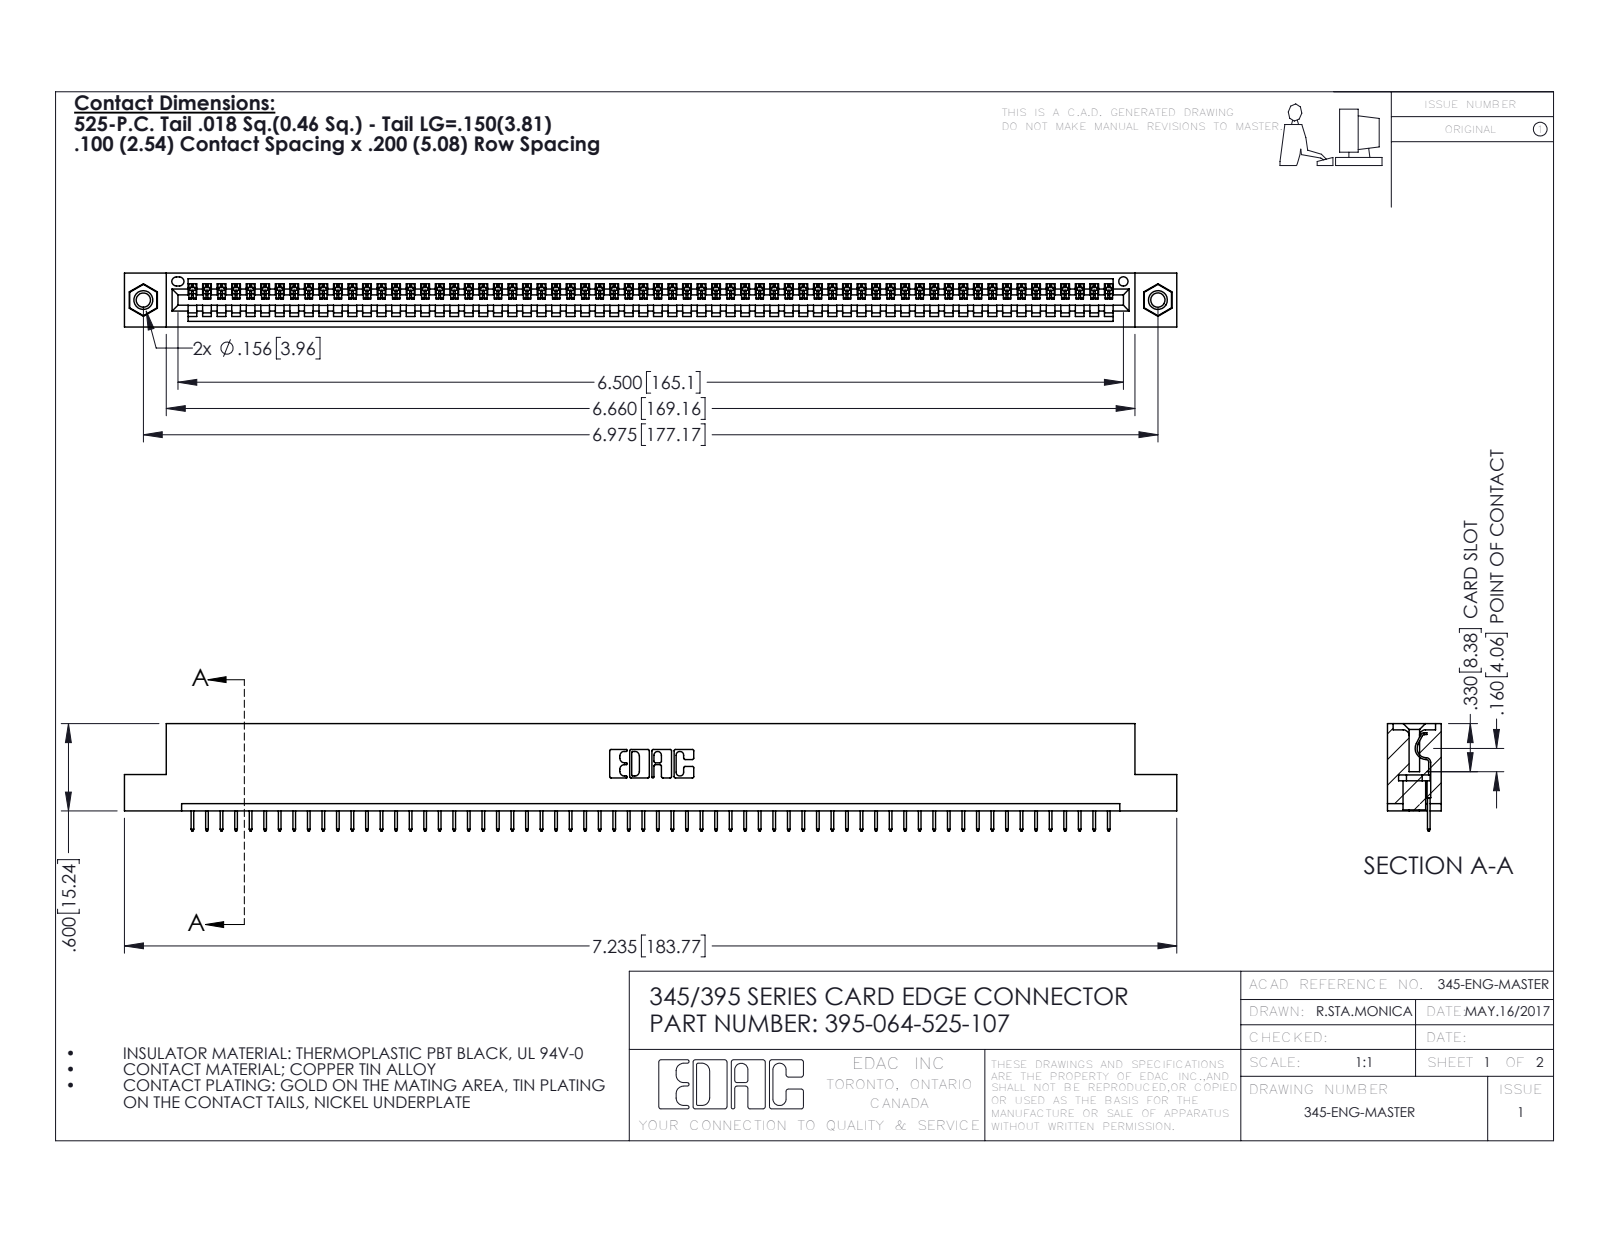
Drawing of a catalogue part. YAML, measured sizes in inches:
part_name: "395-064-525-107; 345-292-001_345-293-125; 345 Part_Flush Mounting Lugs - 0.156 Dia-TI; 345-250-001_345-250-005-103"
step_written_by: "SolidWorks 2020 (CONFIG_CONTROL_DESIGN)"
units: inches
bodies: {solids: 67, faces: 4154, planar: 3056, cylindrical: 1082, other: 16}
overall_size: [7.235, 0.737, 0.37]
volume: 1.059
surface_area: 34.92
round_holes:
  - {diameter: 0.098, count: 2}
  - {diameter: 0.125, count: 2}
  - {diameter: 0.156, count: 2}
  - {diameter: 0.064, count: 1}
round_bosses_or_shafts:
  - {diameter: 0.155, count: 2}
partial_cylinders:
  - {radius: 0.006, count: 128}
  - {radius: 0.01, count: 22}
  - {radius: 0.007, count: 6}
  - {radius: 0.031, count: 6}
  - {radius: 0.026, count: 3}
  - {radius: 0.031, count: 2}
  - {radius: 0.04, count: 2}
  - {radius: 0.014, count: 1}
face_to_face_distances: [0.072, 0.298, 0.37, 0.2, 0.098, 0.272, 0.025, 0.225, 0.072, 0.149]
hole_center_spacings: [0.27, 6.739, 6.975]
